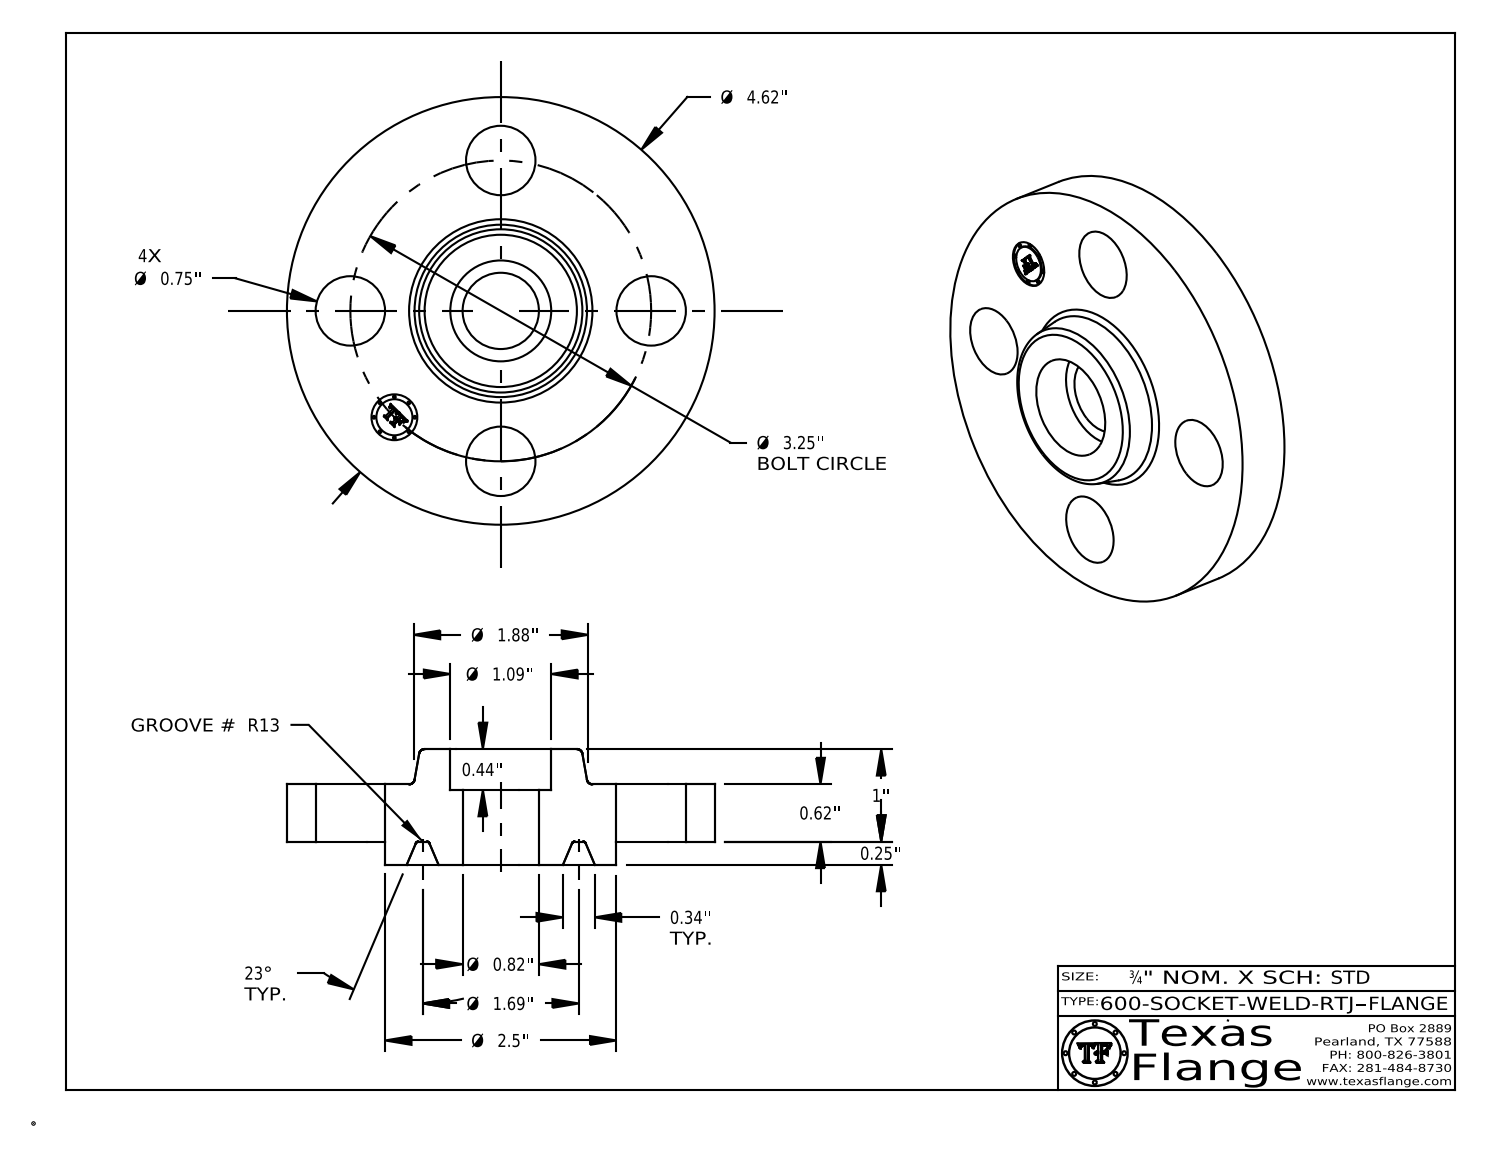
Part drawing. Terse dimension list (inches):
name: 600-SOCKET-WELD-RTJ
written by: CATIA V5 STEP AP214 (AUTOMOTIVE_DESIGN)
unit: in
bodies: 1 solid, 422 faces (372 planar, 36 cylindrical, 14 other)
size: 4.62 × 4.62 × 1.25
volume: 10.35 in³; area: 52.76 in²
holes: 4× ⌀0.75, 1× ⌀0.495, 1× ⌀0.824, 1× ⌀1.09
bosses: 8× ⌀0.03, 1× ⌀4.62, 1× ⌀2.5, 1× ⌀0.39
face distances: 0.62, 0.25, 0.87, 1.25, 1, 0.38, 0.81, 0.56, 0.06, 0.44
hole spacings: 1.625, 2.298, 1.244, 3.003, 3.25
